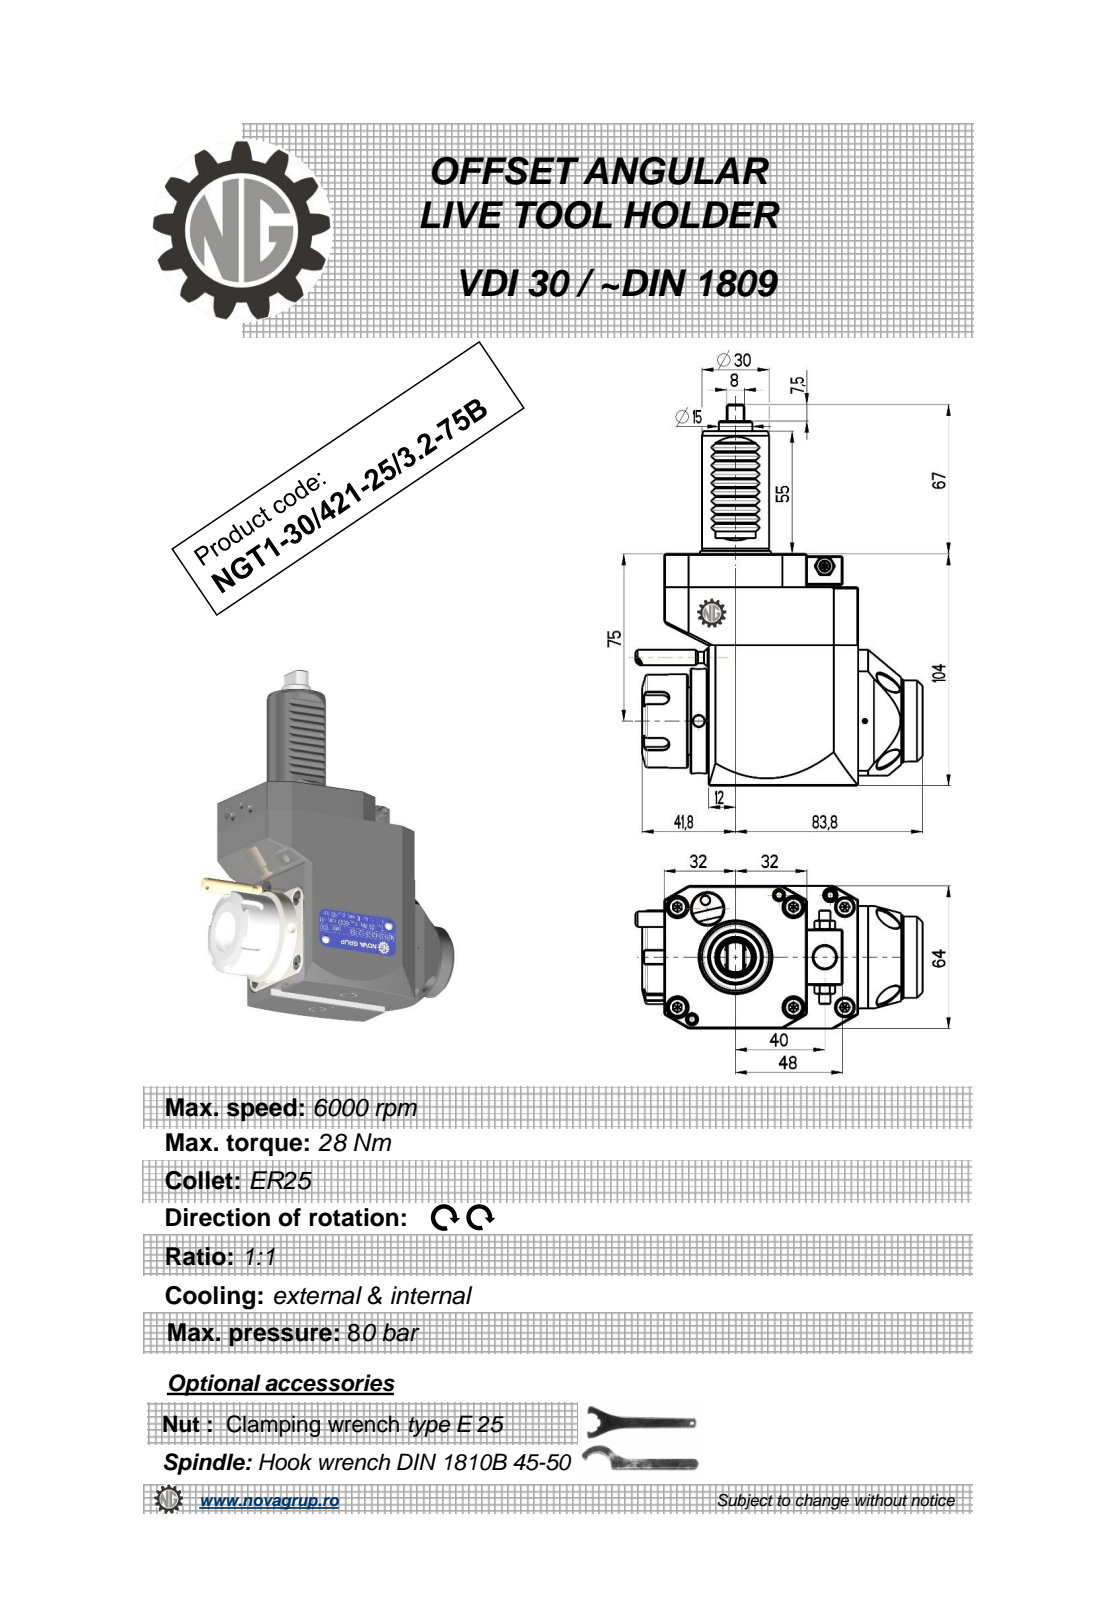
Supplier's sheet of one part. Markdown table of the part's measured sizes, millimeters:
| quantity | value |
| --- | --- |
| part name | NGT1_30_421_25_3_2_75B |
| STEP written by | PRO/ENGINEER BY PARAMETRIC TECHNOLOGY CORPORATION, 2010280 (CONFIG_CONTROL_DESIGN) |
| units | millimeters |
| bodies | 1 solid, 436 faces (202 planar, 86 cylindrical, 148 other) |
| overall size | 171 × 128.63 × 64 |
| volume | 587 708 mm³ |
| surface area | 56 258 mm² |
| round holes (diameter × count) | 5 × 2, 2.5 × 1, 3 × 1, 4.2 × 1, 9.5 × 1, 10 × 1, 20.3 × 1 |
| round bosses / shafts (diameter × count) | 5 × 2, 47 × 1, 42 × 1, 36.5 × 1, 35 × 1, 30 × 1, 15 × 1, 8.96 × 1 |
| partial cylindrical surfaces (radius × count) | 0.26 × 12, 0.3 × 10, 3 × 5, 0.8 × 2, 160 × 2, 7.2 × 1, 32 × 1 |
| main face-to-face distances | 64, 104, 87, 15, 89, 19.8, 0.5, 20, 67.2, 67 |
| hole center spacings | 33.19, 43, 56.45, 68, 89.54 |
